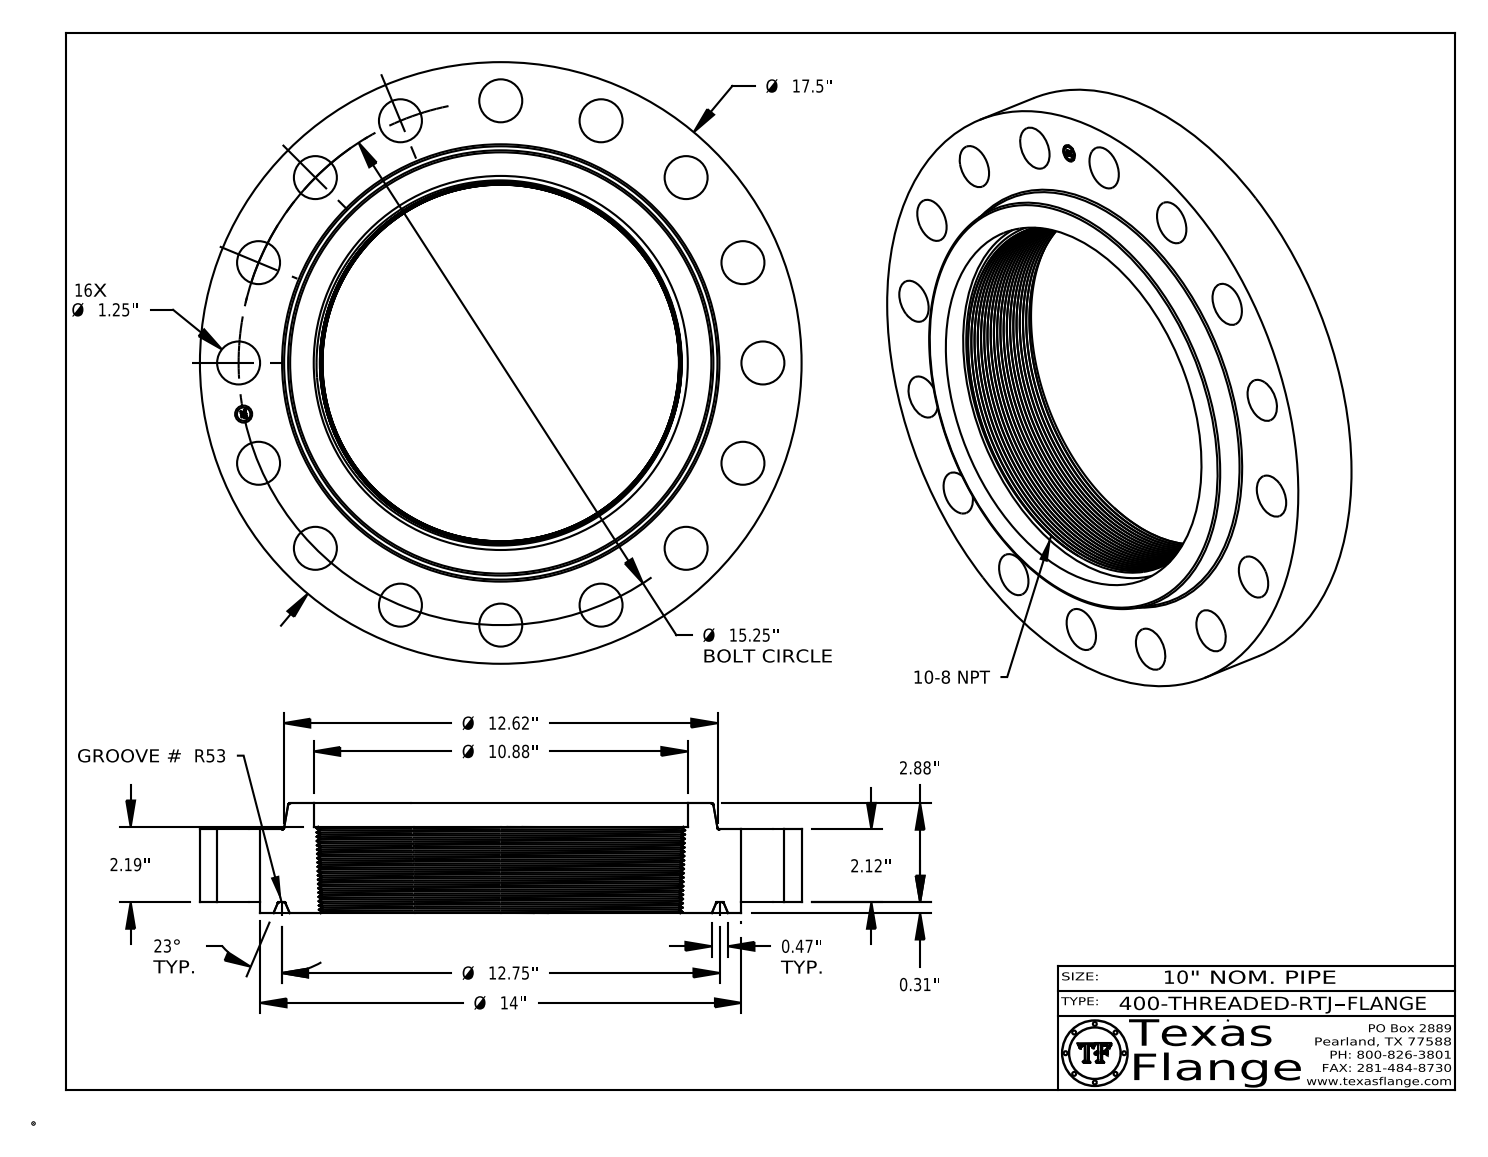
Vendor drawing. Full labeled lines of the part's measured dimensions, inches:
Part name (STEP PRODUCT): 400-THREADED-RTJ
STEP written by: CATIA V5 STEP AP214 (AUTOMOTIVE_DESIGN)
Units: inches
Bodies: 1 solid, 652 faces (372 planar, 58 cylindrical, 222 other)
Overall size (bounding box): 17.5 × 17.5 × 3.193
Volume: 322.7 in³ · Surface area: 749.8 in²
Round holes (diameter × count): ⌀1.25 ×16, ⌀0.495 ×1, ⌀10.88 ×1
Round bosses / shafts (diameter × count): ⌀0.03 ×8, ⌀17.5 ×1, ⌀14 ×1, ⌀0.39 ×1
Main face-to-face distances: 2.12, 0.313, 2.433, 3.193, 2.88, 0.76, 0.07, 2.503, 2.19, 0.69
Hole centre spacings: 8.472, 10.783, 14.957, 14.089, 7.625, 2.975, 2.975, 5.836
